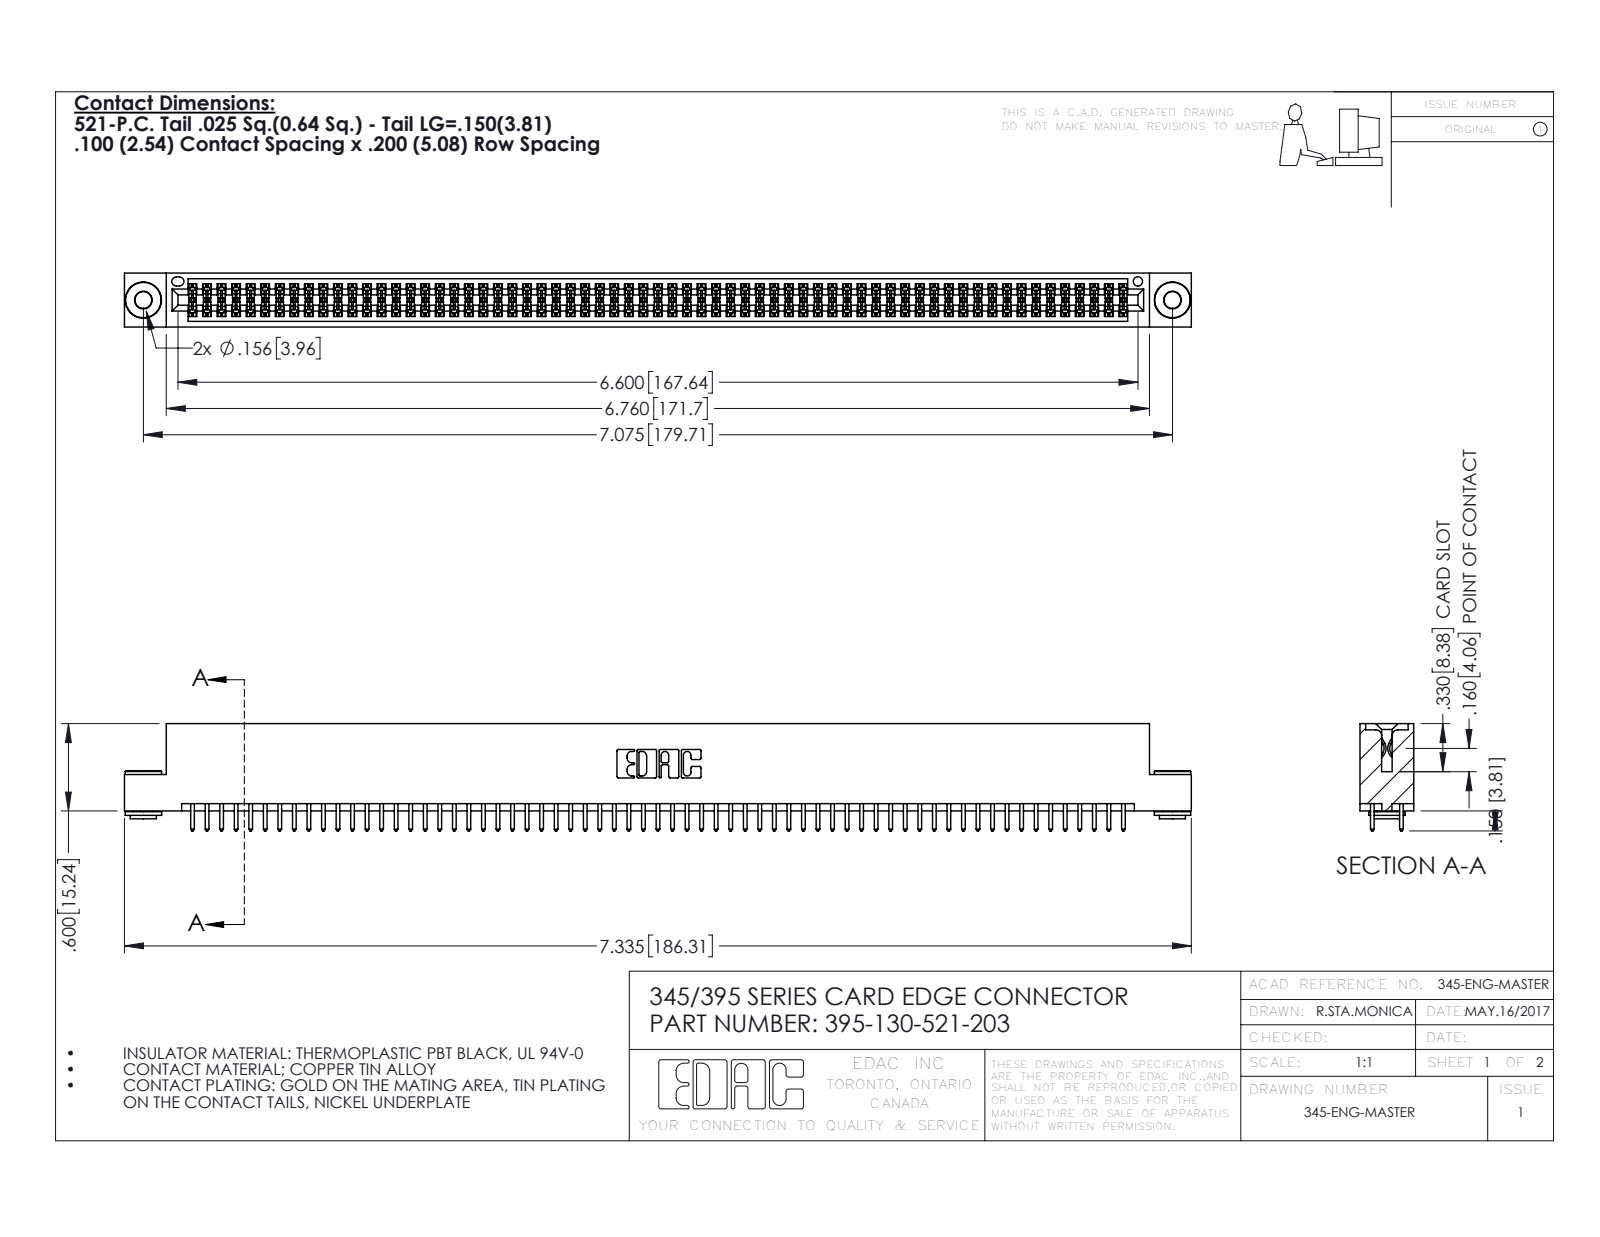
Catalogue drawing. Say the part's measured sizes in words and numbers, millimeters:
The part is named "345-292-001_345-293-121; 345 Part_Flush Mounting Lugs - 0.156 Dia-TH; 395-130-521-203; 345-250-002_345-250-002-102". Its 3-D file was written by "SolidWorks 2016 (CONFIG_CONTROL_DESIGN)". It is 133 solids with 6664 faces: 4380 planar, 2276 cylindrical and 8 other. Overall it measures 186.3 by 18.7 by 9.4 millimeters. Its volume is 18 270 cubic millimeters and its surface area 27 320 square millimeters. Round holes: 2 of diameter 2.9, 2 of diameter 4, 1 of diameter 1.6. Round bosses or shafts: 2 of diameter 6.4, 2 of diameter 4.6, 2 of diameter 3.5. Partial cylindrical surfaces (rounded edges, fillets, slot ends): 195 of radius 0.2, 130 of radius 0.3, 22 of radius 0.3, 6 of radius 0.2, 6 of radius 0.8, 3 of radius 0.7, 2 of radius 0.4, 2 of radius 0.5. The main face-to-face distances are 1.8, 7.6, 5.1, 0.6, 2.5, 6.9, 9.4, 5.7, 4.4, 3.8. The hole center spacings are 6.9, 173.7, 179.7.
